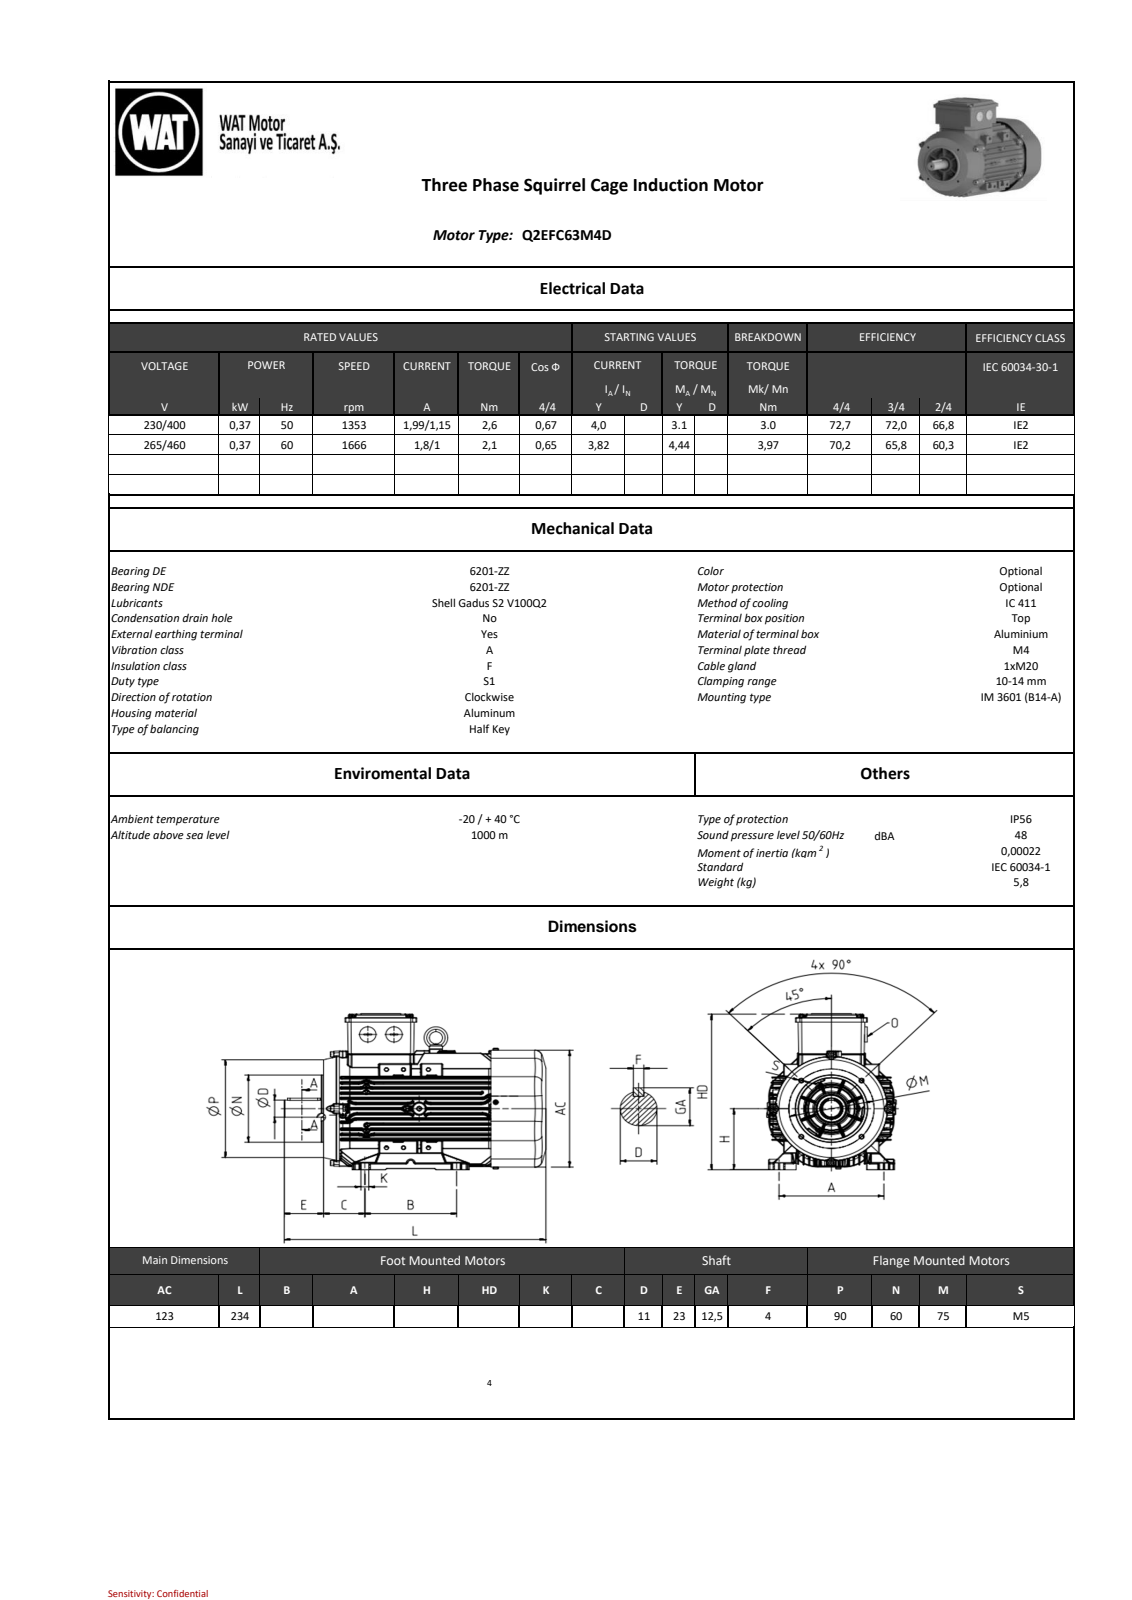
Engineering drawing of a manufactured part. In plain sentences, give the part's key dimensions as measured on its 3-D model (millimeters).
The part is named "QE Series_ 63_B14a_Deep Cover__stp_objects". Its 3-D file was written by "SIEMENS PLM Software NX2206.8101 (AP203_CONFIGURATION_CONTROLLED_3D_DESIGN_OF_MECHANICAL_PARTS_AND_ASSEMBLIES_MIM_LF)". It is 0 solids with 1240 faces: 766 planar, 356 cylindrical and 118 other. Overall it measures 233.47 by 160.6 by 126.28 millimeters. Round holes: 8 of diameter 3.65, 4 of diameter 2.5, 4 of diameter 3.3, 4 of diameter 3.8, 3 of diameter 3, 1 of diameter 5, 1 of diameter 8, 1 of diameter 14.96, 1 of diameter 19, 1 of diameter 19.84, 1 of diameter 57. Round bosses or shafts: 8 of diameter 8, 4 of diameter 4.8, 2 of diameter 4, 1 of diameter 123, 1 of diameter 121, 1 of diameter 61, 1 of diameter 60, 1 of diameter 25.28. Partial cylindrical surfaces (rounded edges, fillets, slot ends): 104 of radius 0.5, 49 of radius 1, 16 of radius 1.5, 12 of radius 4, 7 of radius 0.1, 6 of radius 0.3, 6 of radius 2, 6 of radius 8. The main face-to-face distances are 7.02, 27.96, 28.05, 6.93, 13.81, 5, 6.88, 21.03, 14.16, 7.06. The hole center spacings are 37.5, 54, 63, 82.98, 10, 75, 5, 16.98.
